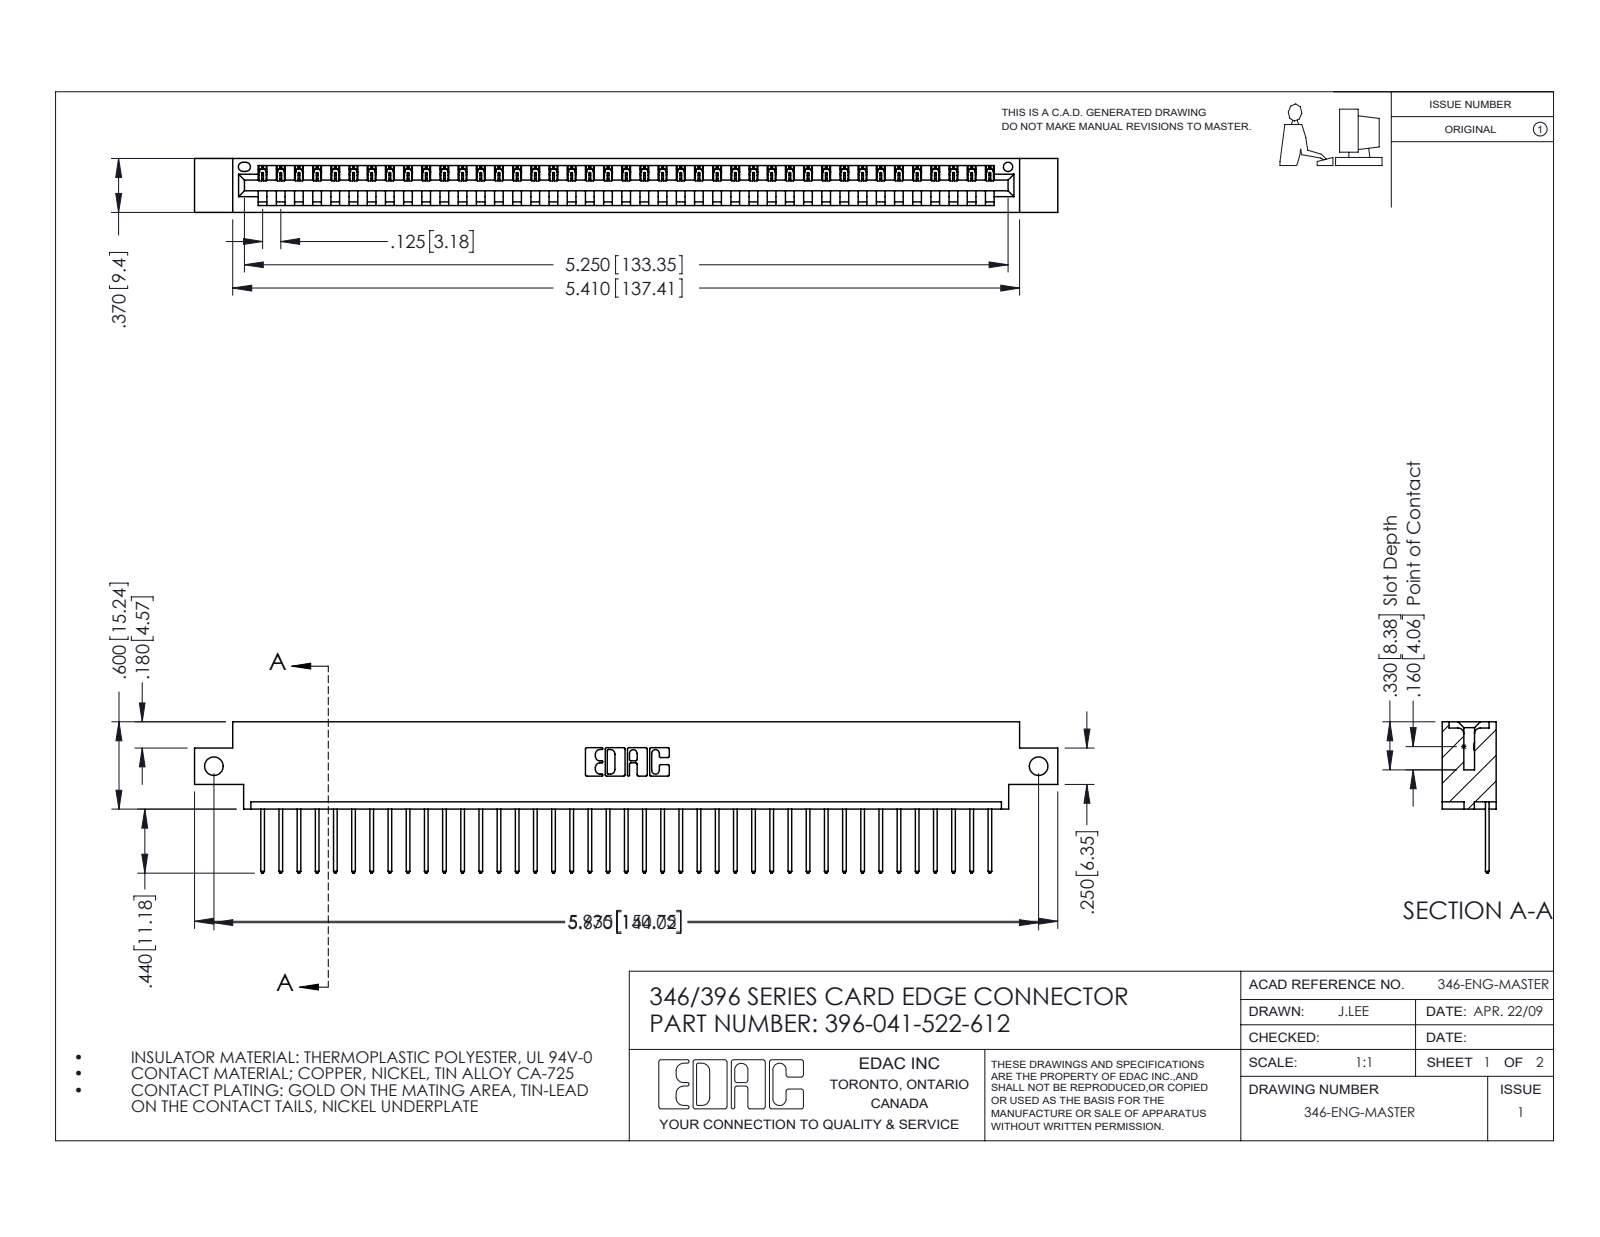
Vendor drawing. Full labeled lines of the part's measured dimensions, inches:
Part name (STEP PRODUCT): 396-041-522-612; 345-292-001_345-293-122; 346 Part_0.170 Offset - Side Mount
STEP written by: SolidWorks 2016 (CONFIG_CONTROL_DESIGN)
Units: inches
Bodies: 42 solids, 2504 faces (1720 planar, 784 cylindrical, 0 other)
Overall size (bounding box): 5.935 × 1.04 × 0.37
Volume: 0.866 in³ · Surface area: 27.72 in²
Round holes (diameter × count): ⌀0.128 ×2, ⌀0.064 ×1
Partial cylindrical surfaces — rounded edges, fillets, slot ends (radius × count): R0.006 ×82, R0.01 ×82, R0.01 ×22, R0.007 ×6, R0.031 ×6, R0.026 ×3, R0.031 ×2, R0.04 ×2
Main face-to-face distances: 0.048, 0.322, 0.37, 0.25, 0.072, 0.298, 0.025, 0.148, 0.222, 0.1
Hole centre spacings: 5.67
